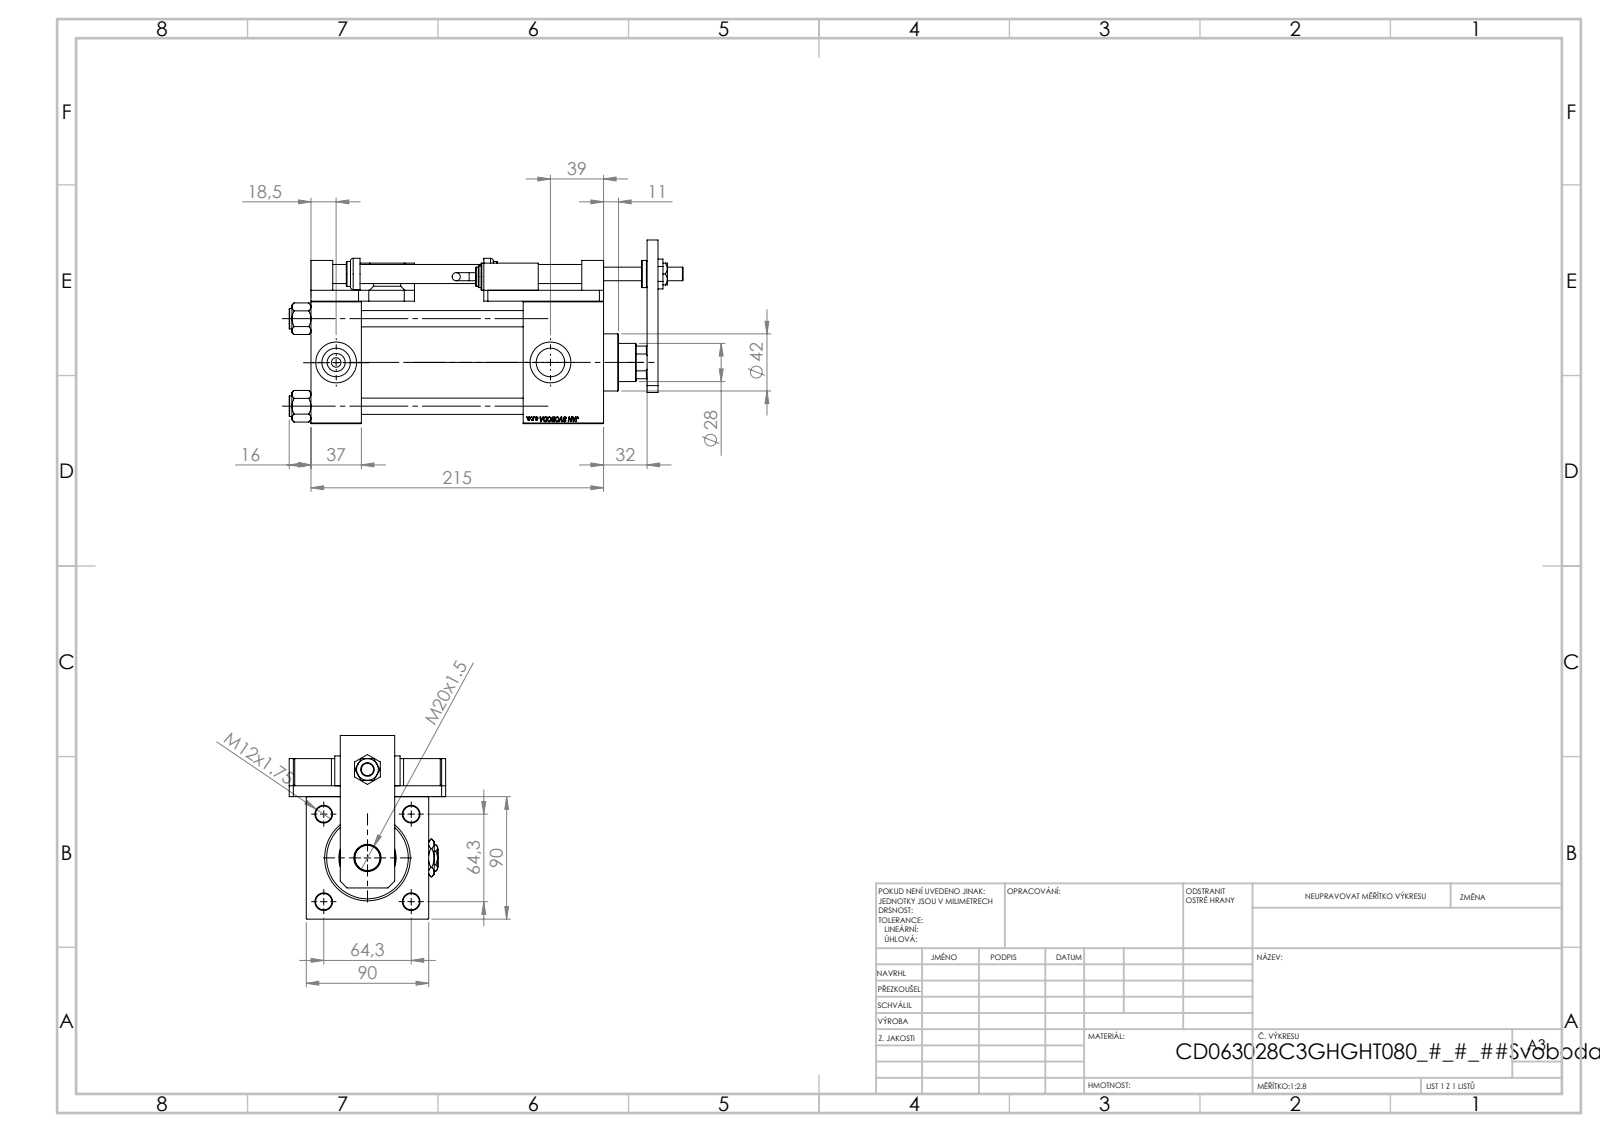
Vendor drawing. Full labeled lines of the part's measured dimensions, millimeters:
Part name (STEP PRODUCT): V215CD_Body_C; V215CD_VCP_C; V215CD_VC_C; V215CD_SWITCH_Q_BLOK (+8 more)
STEP written by: SolidWorks 2019 (CONFIG_CONTROL_DESIGN)
Units: millimetres
Bodies: 26 solids, 1478 faces (695 planar, 166 cylindrical, 617 other)
Overall size (bounding box): 289.5 × 135 × 115
Volume: 1 316 000 mm³ · Surface area: 311 002 mm²
Round holes (diameter × count): ⌀8.5 ×4, ⌀12 ×4, ⌀13.5 ×4, ⌀7 ×2, ⌀20.96 ×2, ⌀30 ×2, ⌀10 ×1, ⌀14 ×1, ⌀18.5 ×1, ⌀20 ×1, ⌀28 ×1, ⌀31 ×1
Round bosses / shafts (diameter × count): ⌀15 ×4, ⌀20 ×3, ⌀16 ×2, ⌀14 ×2, ⌀6 ×2, ⌀69 ×1, ⌀42 ×1, ⌀23 ×1
Partial cylindrical surfaces — rounded edges, fillets, slot ends (radius × count): R7.5 ×4, R13.5 ×1
Main face-to-face distances: 8, 90, 37, 98, 215, 178, 40, 32, 91, 59
Hole centre spacings: 45.47, 64.3, 32, 45.96, 90.93, 102.33, 199, 201.56
